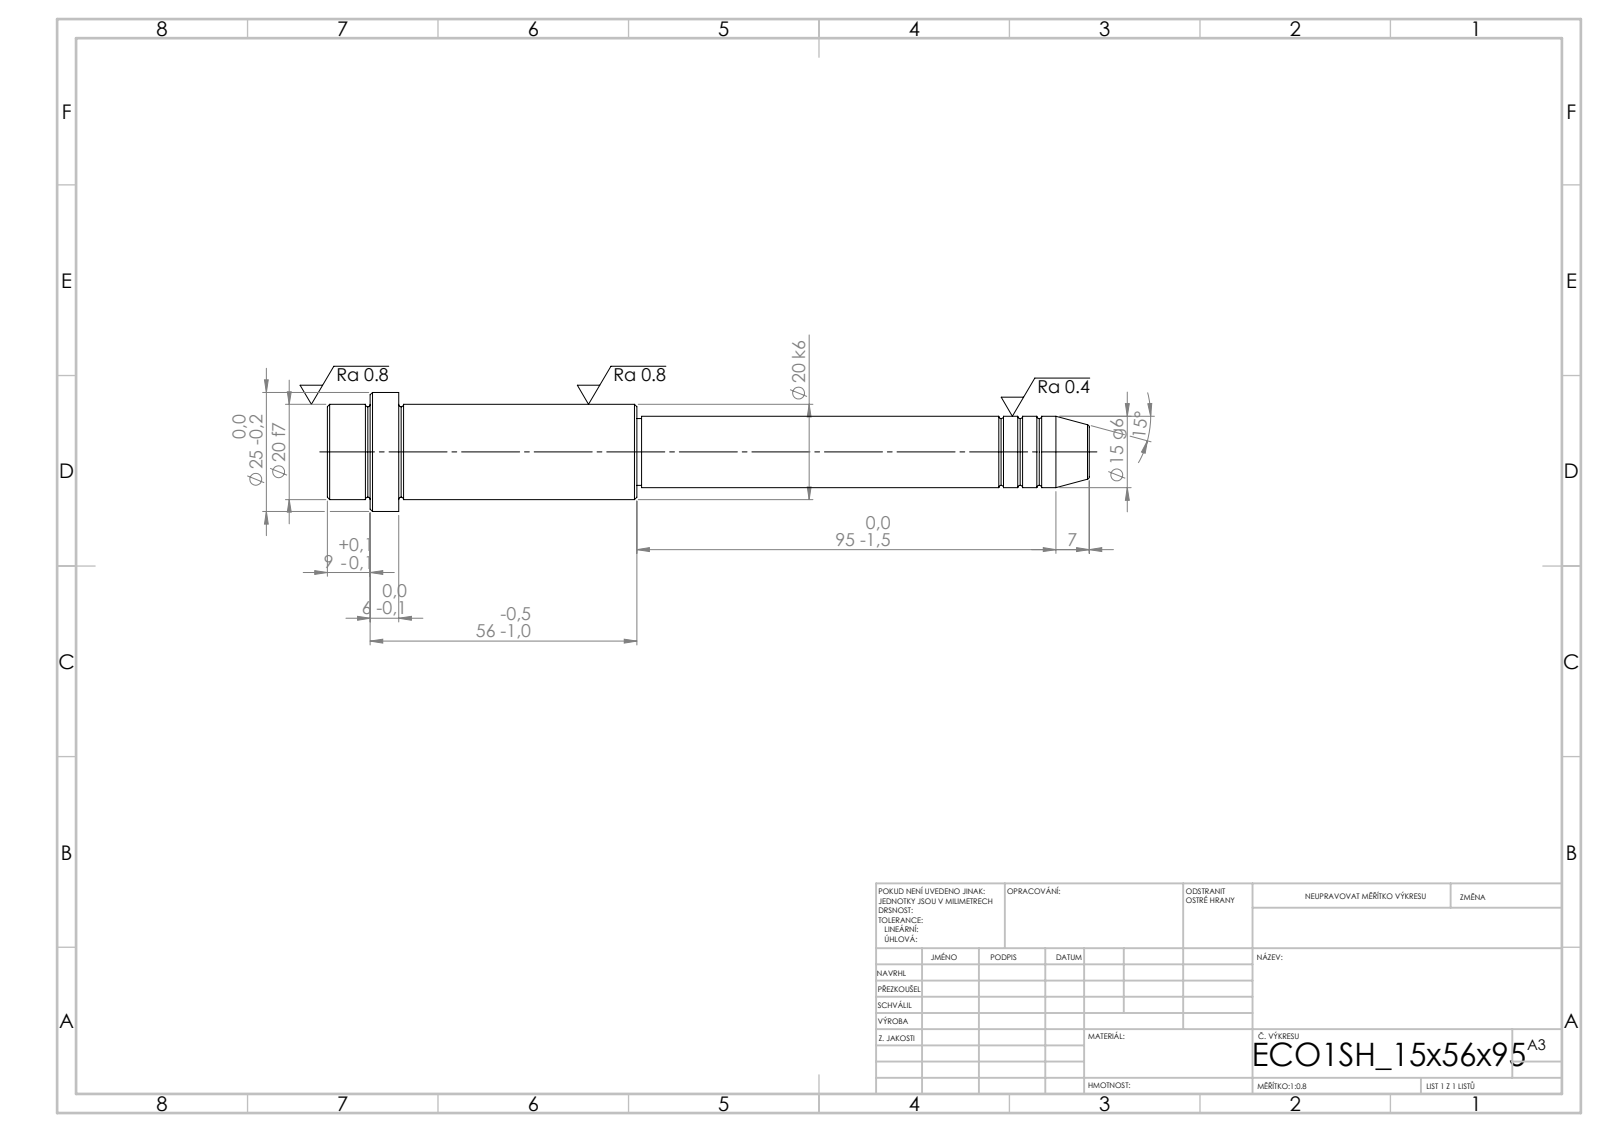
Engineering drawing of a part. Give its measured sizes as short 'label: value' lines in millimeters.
written by: SolidWorks 2019 (CONFIG_CONTROL_DESIGN)
unit: mm
bodies: 1 solid, 52 faces (6 planar, 16 cylindrical, 30 other)
size: 160 × 25 × 25
volume: 37 834 mm³; area: 9 643 mm²
bosses: 1× ⌀25, 1× ⌀20, 1× ⌀15, 1× ⌀14
face distances: 15, 6, 9, 50, 56, 65, 95, 145, 151, 160
